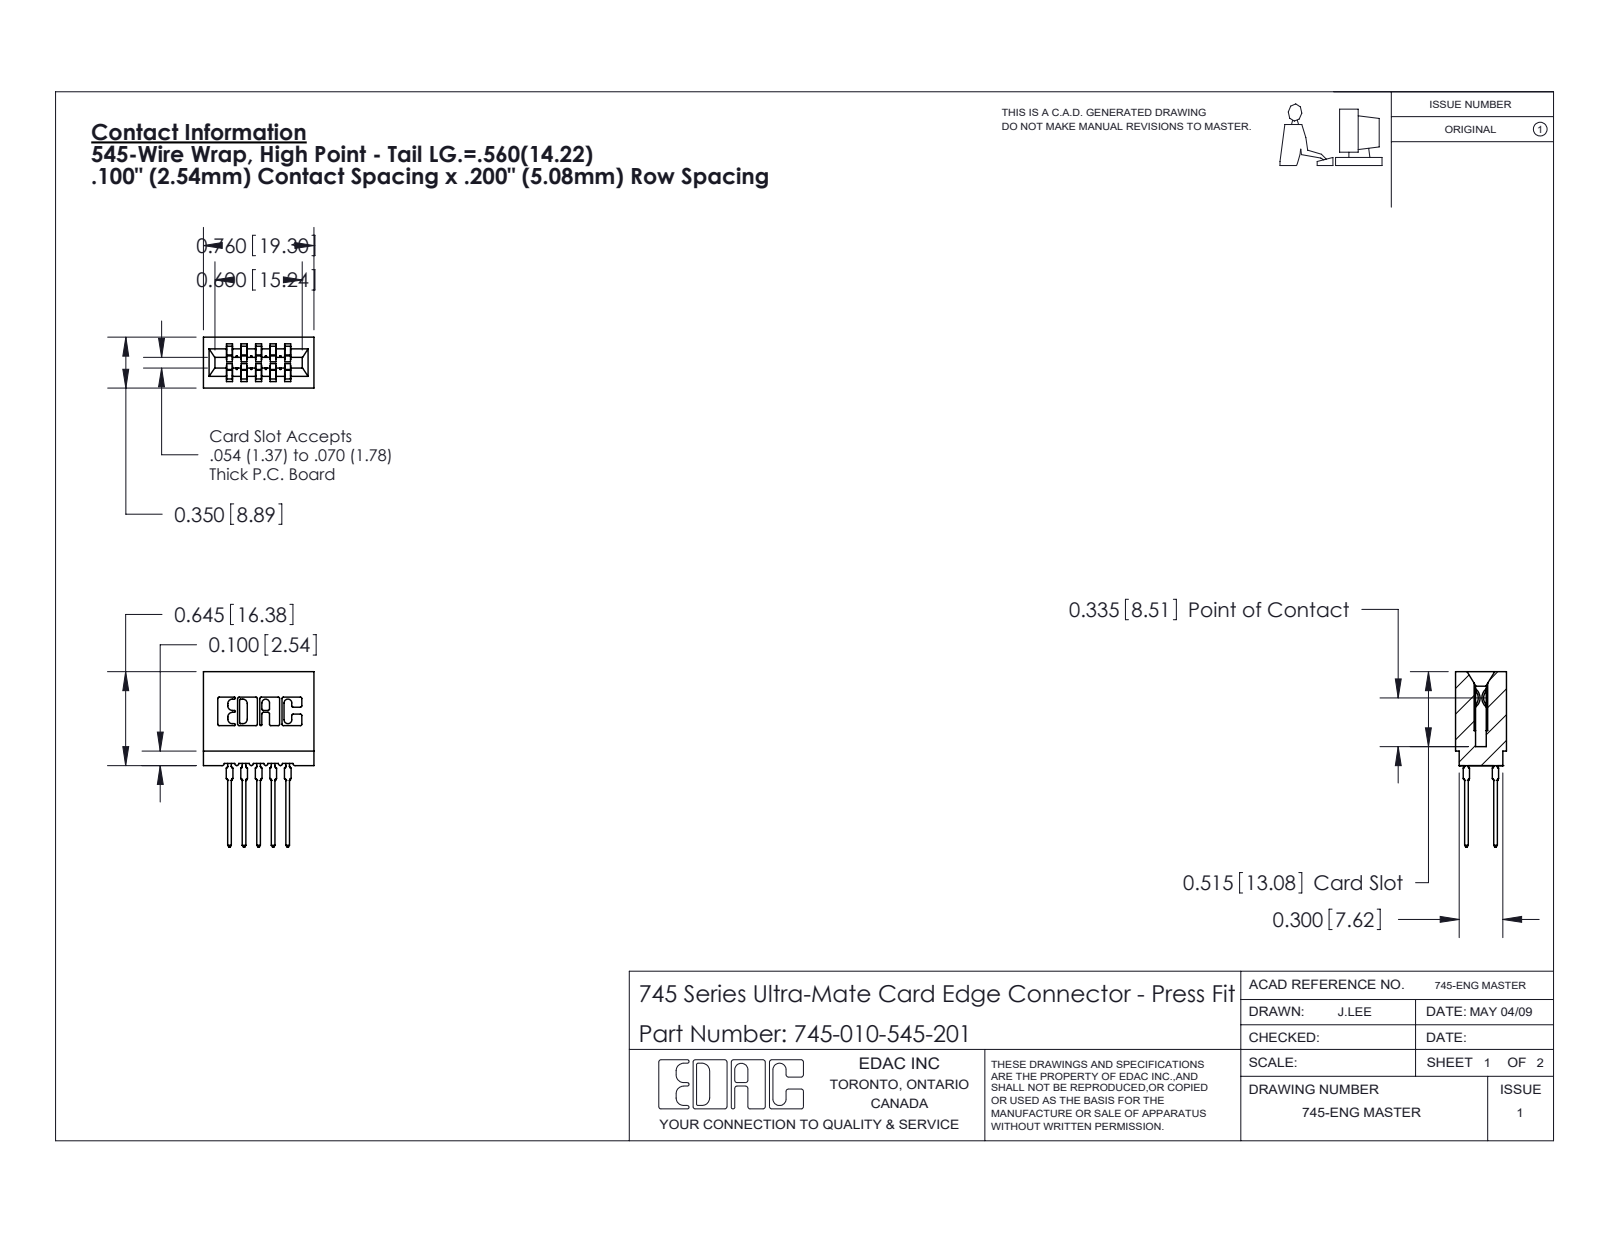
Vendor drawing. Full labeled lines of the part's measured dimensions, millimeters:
Part name (STEP PRODUCT): 745 Part_Insulator Option - 01; 745-292-001_545; 745-010-545-201
STEP written by: SolidWorks 2020 (CONFIG_CONTROL_DESIGN)
Units: millimetres
Bodies: 11 solids, 990 faces (515 planar, 215 cylindrical, 260 other)
Overall size (bounding box): 30.6 × 19.3 × 8.9
Volume: 2 000 mm³ · Surface area: 3 356 mm²
Partial cylindrical surfaces — rounded edges, fillets, slot ends (radius × count): R0.3 ×22, R0.5 ×20, R0.4 ×10, R0.1 ×8, R0.3 ×8, R0.2 ×6, R0.8 ×6, R0.7 ×3
Main face-to-face distances: 2.5, 5.1, 1.1, 7.6, 3.6, 1.5, 7.3, 8.9, 1.6, 6.1
